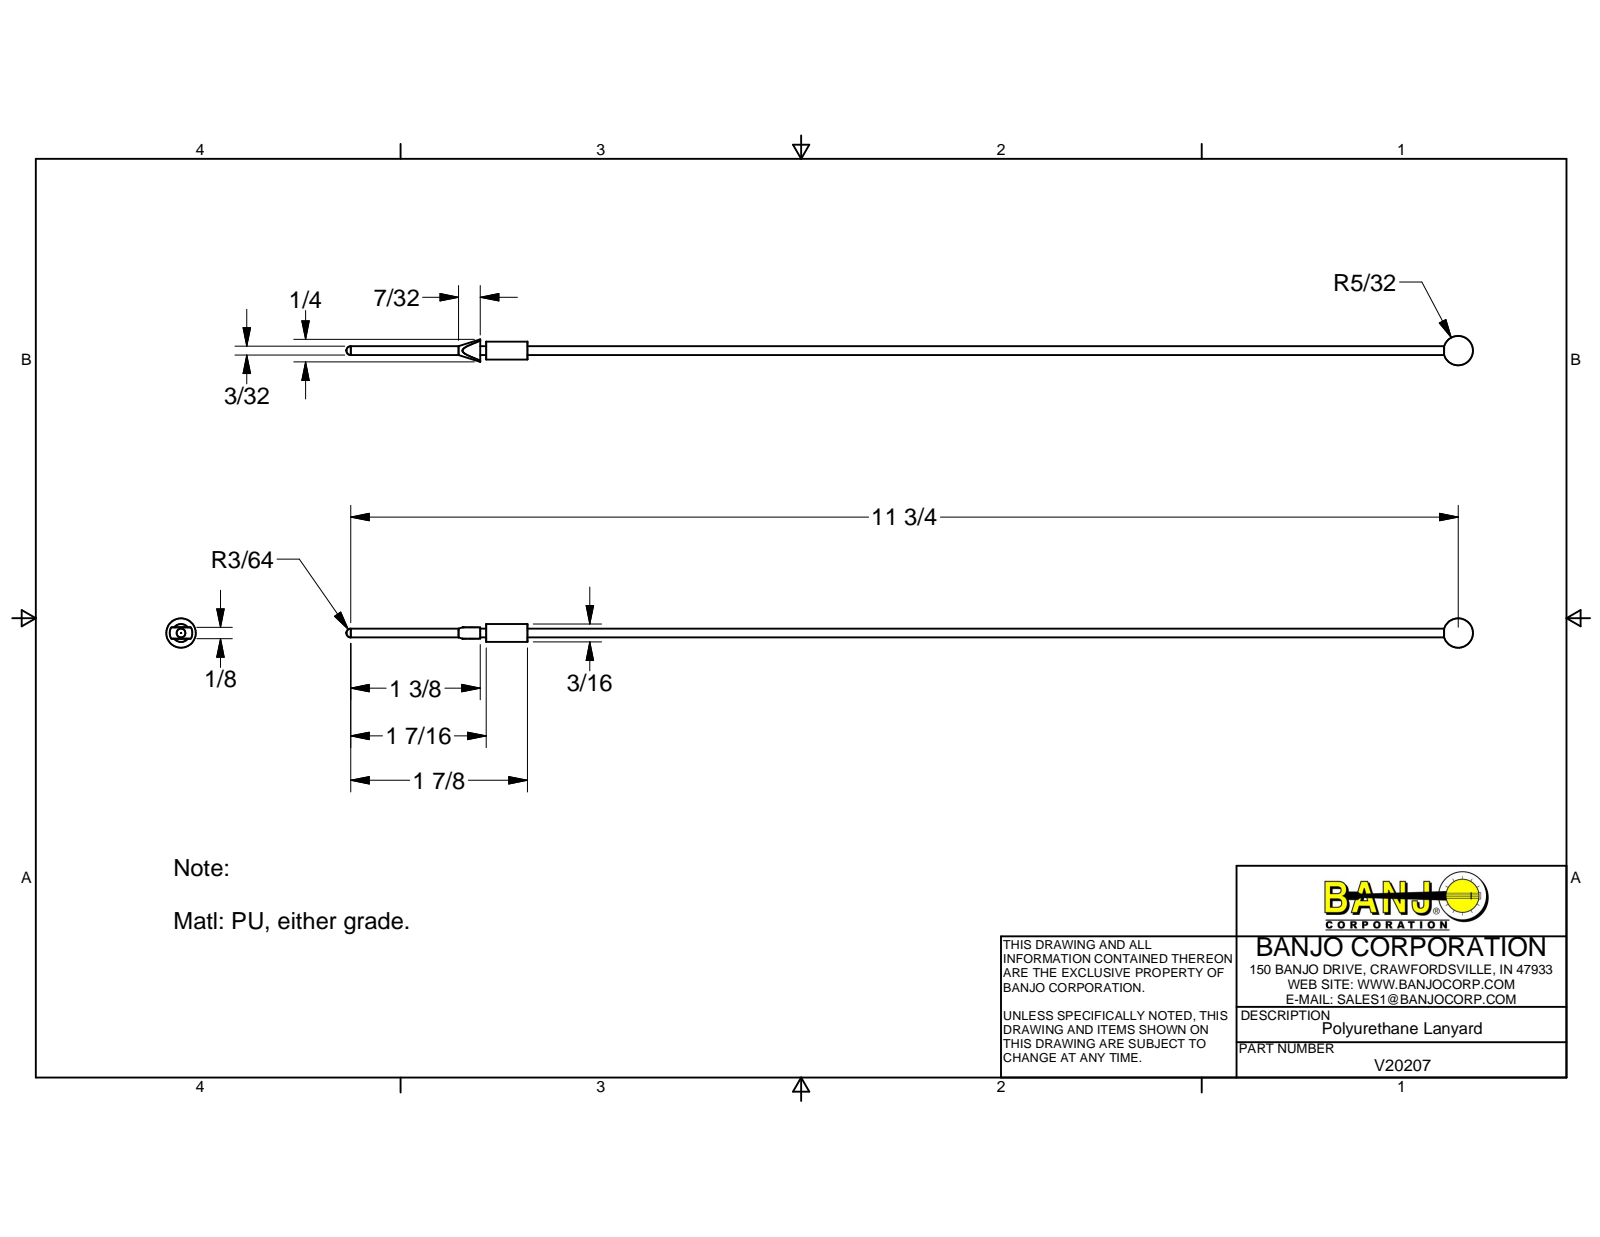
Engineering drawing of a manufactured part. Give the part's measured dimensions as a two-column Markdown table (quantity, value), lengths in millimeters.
| quantity | value |
| --- | --- |
| part name | V20207 |
| STEP written by | Autodesk Inventor 2014 (AUTOMOTIVE_DESIGN) |
| units | millimeters |
| bodies | 1 solid, 13 faces (6 planar, 4 cylindrical, 3 other) |
| overall size | 303.56 × 7.94 × 7.94 |
| volume | 1 772 mm³ |
| surface area | 2 564 mm² |
| round bosses / shafts (diameter × count) | 4.83 × 1, 2.38 × 1 |
| main face-to-face distances | 3.04, 11.11, 12.7, 1.59, 48.77, 37.66, 36.07 |
